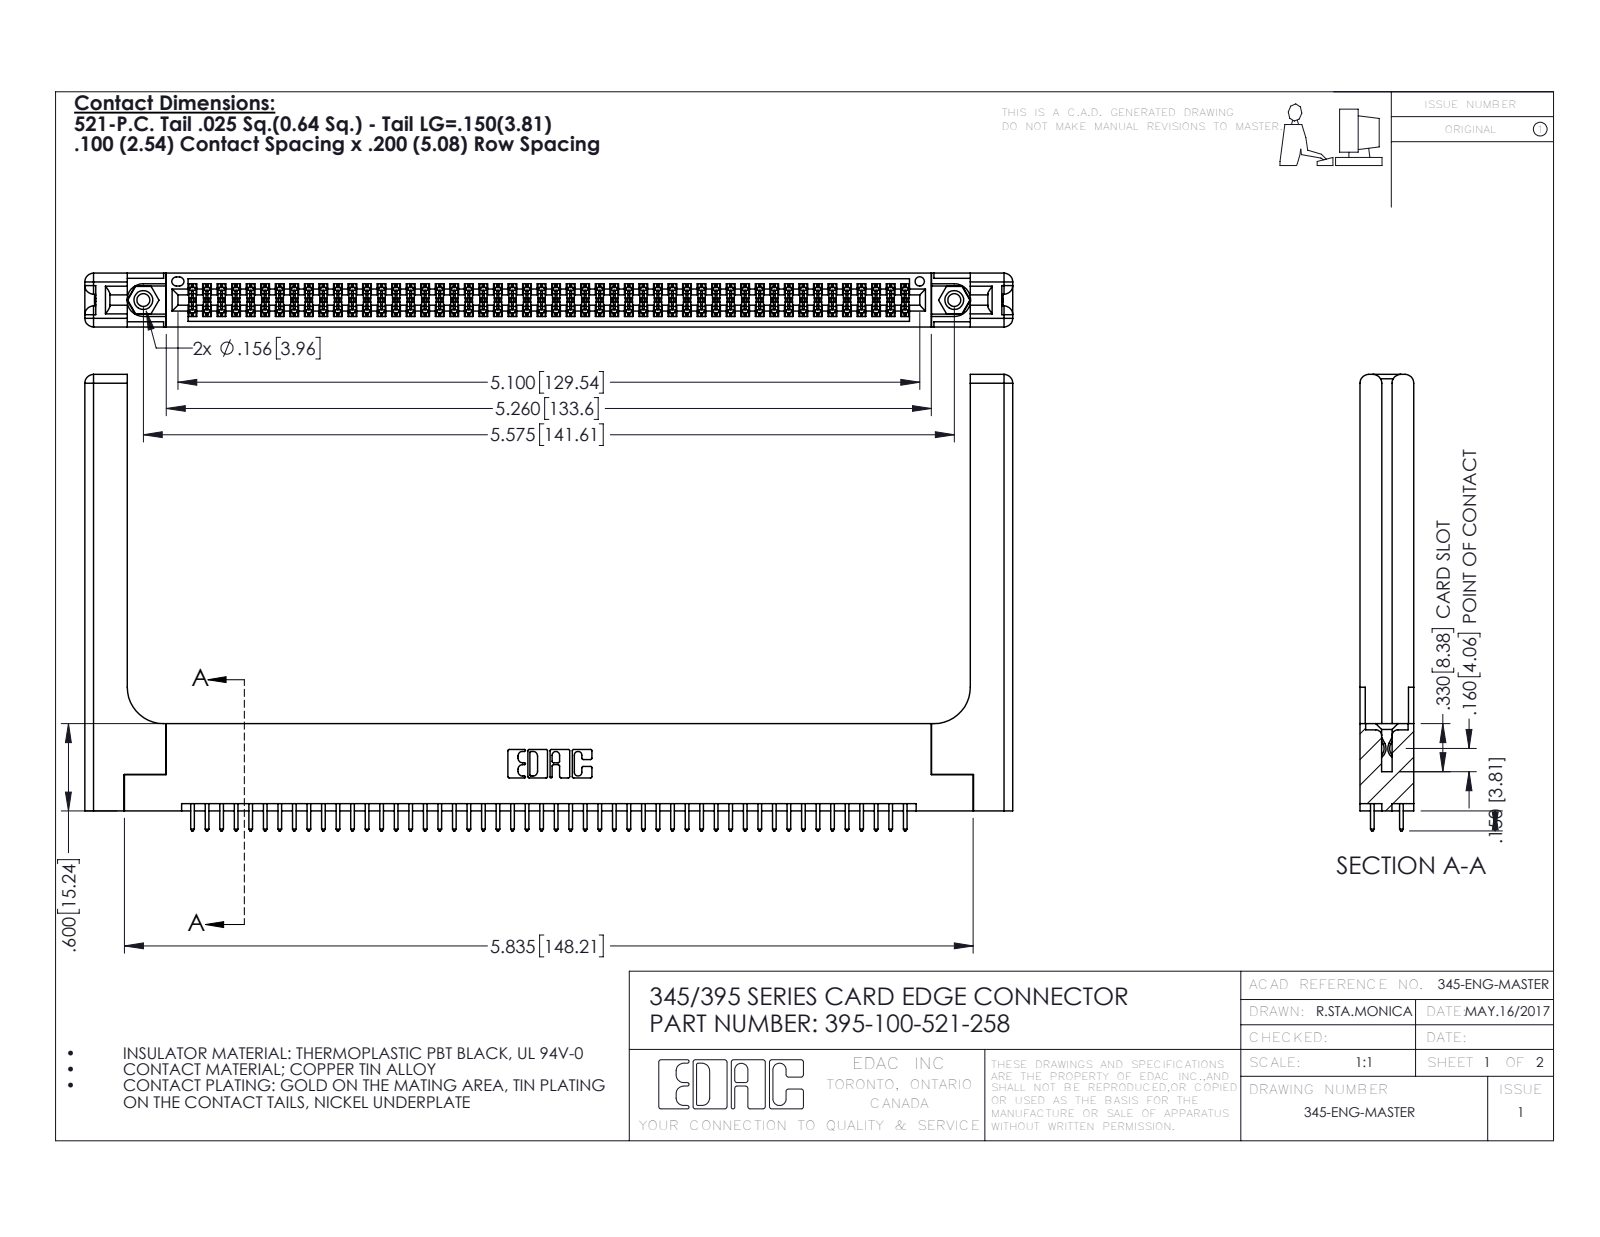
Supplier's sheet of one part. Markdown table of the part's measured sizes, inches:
| quantity | value |
| --- | --- |
| part name | 345-292-001_345-293-121; 345-220-058_345-220-058; 395-100-521-258; 345-250-001_345-250-001-102 (+1 more) |
| STEP written by | SolidWorks 2016 (CONFIG_CONTROL_DESIGN) |
| units | inches |
| bodies | 105 solids, 5382 faces (3528 planar, 1794 cylindrical, 60 other) |
| overall size | 6.379 × 3.137 × 0.37 |
| volume | 1.48 in³ |
| surface area | 43.81 in² |
| round holes (diameter × count) | 0.089 × 2, 0.125 × 2, 0.156 × 2, 0.064 × 1 |
| round bosses / shafts (diameter × count) | 0.155 × 2 |
| partial cylindrical surfaces (radius × count) | 0.006 × 150, 0.01 × 100, 0.01 × 22, 0.06 × 16, 0.007 × 6, 0.031 × 6, 0.026 × 3, 0.014 × 2 |
| main face-to-face distances | 0.072, 0.298, 0.37, 0.2, 0.098, 0.272, 0.025, 0.225, 0.148, 0.15 |
| hole center spacings | 0.27, 5.339, 5.575 |
